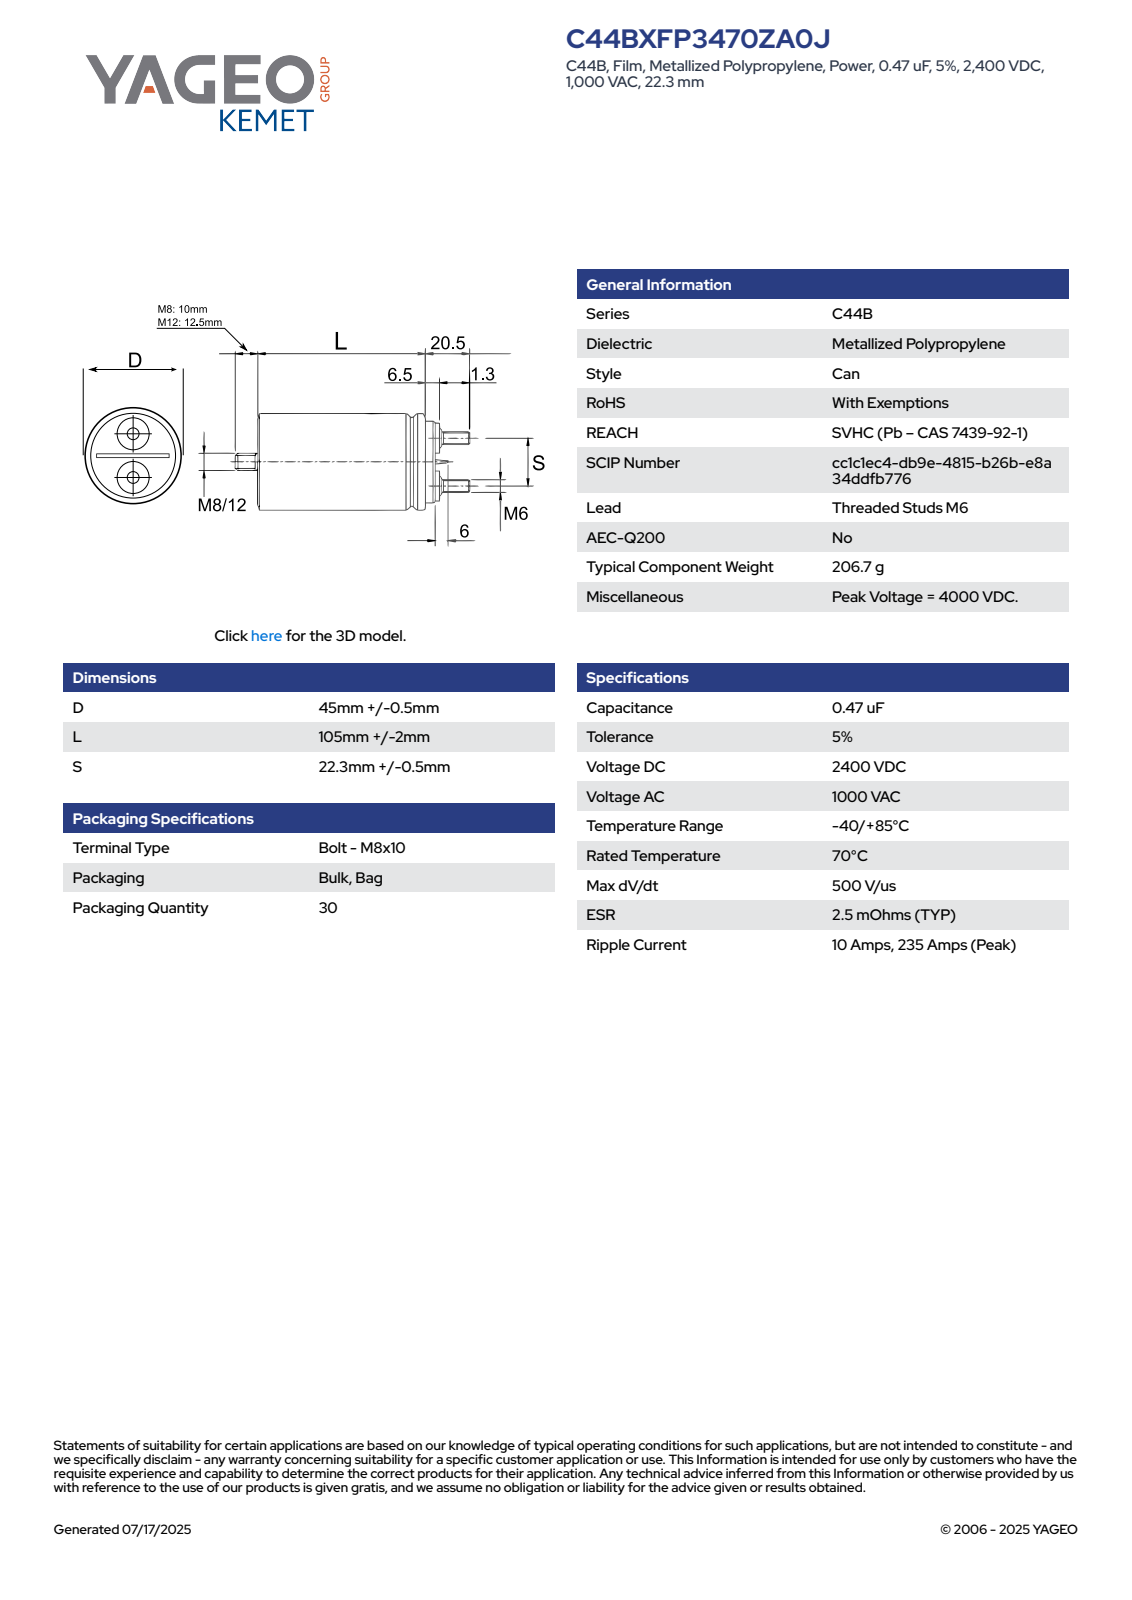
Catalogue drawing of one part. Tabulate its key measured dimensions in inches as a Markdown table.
| quantity | value |
| --- | --- |
| part name | CFP_M6_45X105_D45.5L107S22.8 |
| STEP written by | SolidWorks 2014 (AUTOMOTIVE_DESIGN) |
| units | inches |
| bodies | 1 solid, 117 faces (35 planar, 39 cylindrical, 43 other) |
| overall size | 5.413 × 1.792 × 1.791 |
| volume | 10.92 in³ |
| surface area | 32.25 in² |
| round bosses / shafts (diameter × count) | 0.492 × 2, 0.356 × 2, 0.236 × 2, 1.791 × 1, 1.585 × 1, 0.315 × 1 |
| partial cylindrical surfaces (radius × count) | 0.014 × 1, 0.896 × 1 |
| main face-to-face distances | 4.37, 4.213, 0.157, 0.028, 4.469, 0.256, 0.098, 4.508, 0.295, 0.138 |
